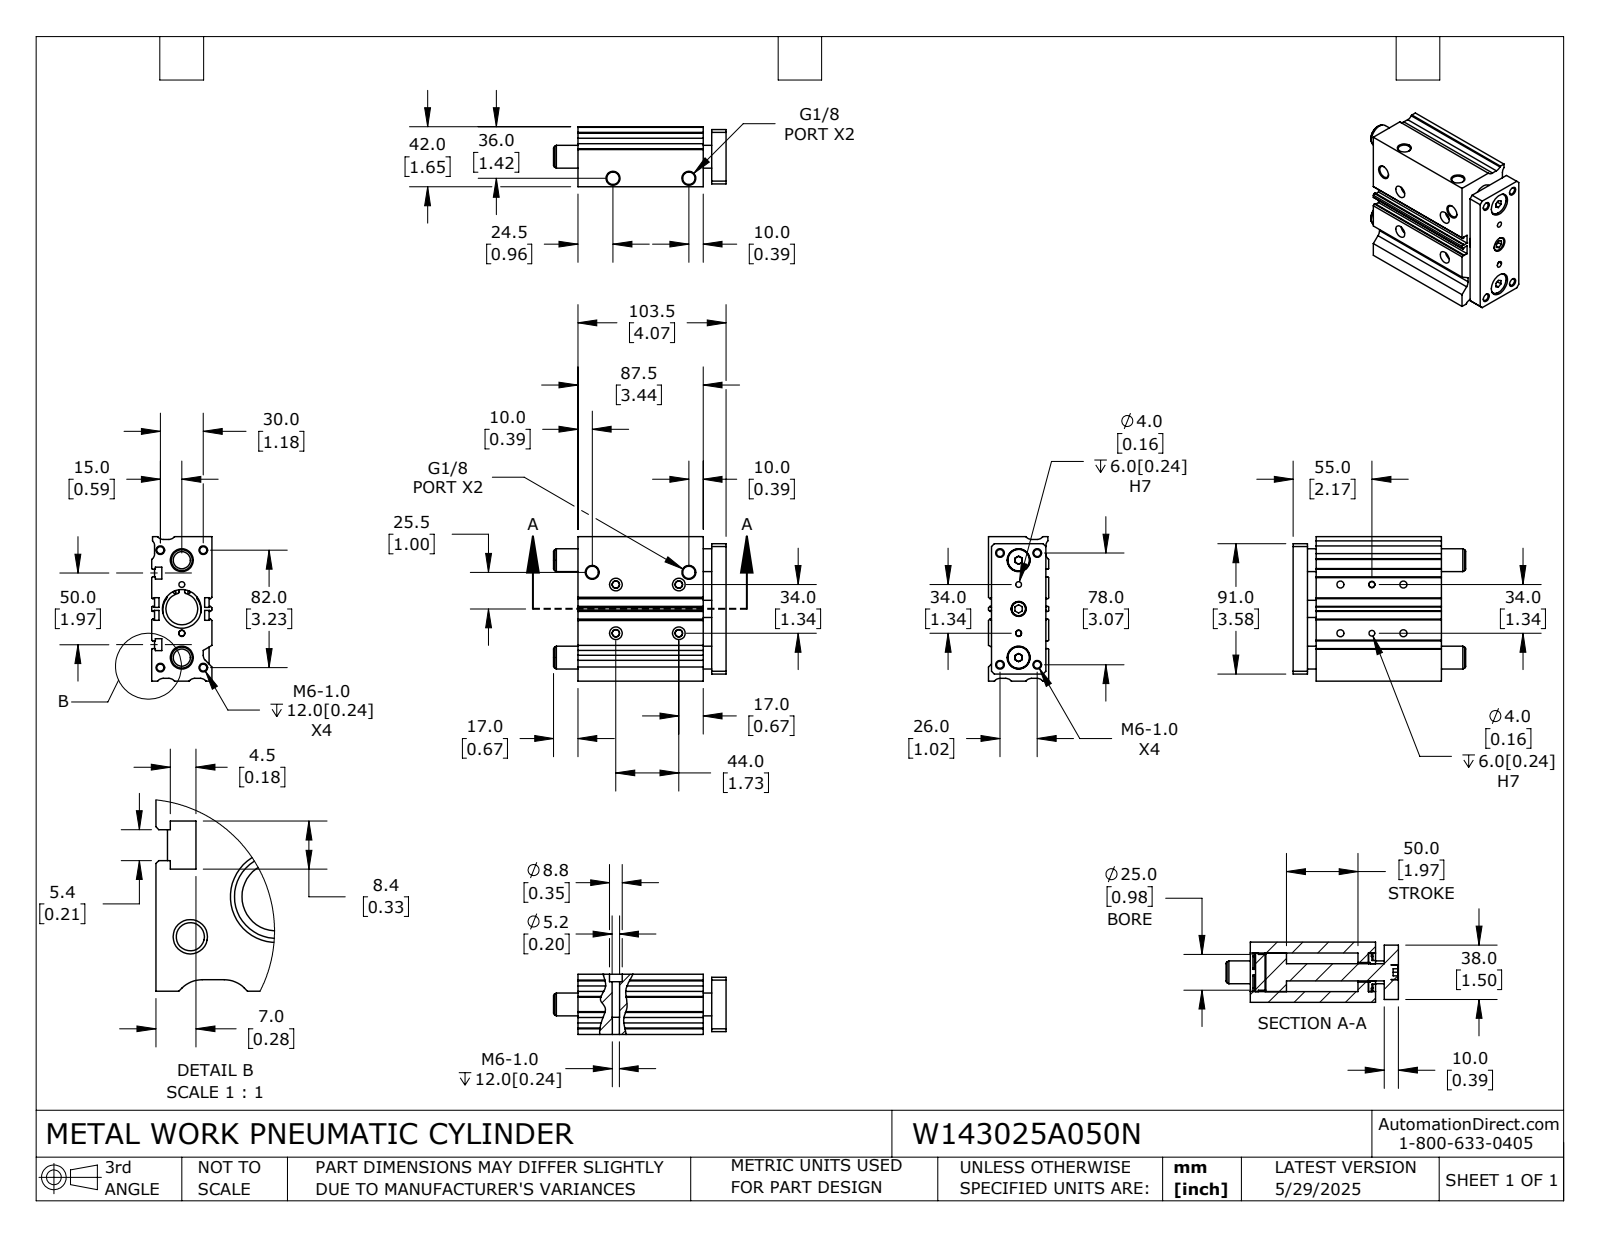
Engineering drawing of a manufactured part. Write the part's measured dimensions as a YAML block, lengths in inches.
part_name: "W143025A050N_ROD; W143025A050N; W143025A050N_BODY"
step_written_by: "SolidWorks 2024 (CONFIG_CONTROL_DESIGN)"
units: inches
bodies: {solids: 6, faces: 390, planar: 191, cylindrical: 157, other: 42}
overall_size: [4.744, 3.976, 1.654]
volume: 21.23
surface_area: 142.8
round_holes:
  - {diameter: 0.194, count: 8}
  - {diameter: 0.067, count: 4}
  - {diameter: 0.157, count: 4}
  - {diameter: 0.194, count: 4}
  - {diameter: 0.205, count: 4}
  - {diameter: 0.337, count: 4}
  - {diameter: 0.346, count: 4}
  - {diameter: 0.63, count: 2}
  - {diameter: 0.413, count: 1}
  - {diameter: 0.472, count: 1}
  - {diameter: 0.539, count: 1}
  - {diameter: 0.874, count: 1}
round_bosses_or_shafts:
  - {diameter: 0.61, count: 2}
  - {diameter: 1.063, count: 1}
  - {diameter: 0.984, count: 1}
  - {diameter: 0.65, count: 1}
  - {diameter: 0.394, count: 1}
partial_cylinders:
  - {radius: 0.039, count: 12}
  - {radius: 0.197, count: 9}
  - {radius: 0.079, count: 8}
  - {radius: 0.524, count: 2}
  - {radius: 0.559, count: 1}
face_to_face_distances: [0.197, 1.654, 0.079, 1.378, 0.236, 0.118, 0.63, 0.394, 4.075, 3.681]
hole_center_spacings: [1.339, 0.111, 0.29, 0.5, 0.548, 0.652, 0.669, 0.866]
